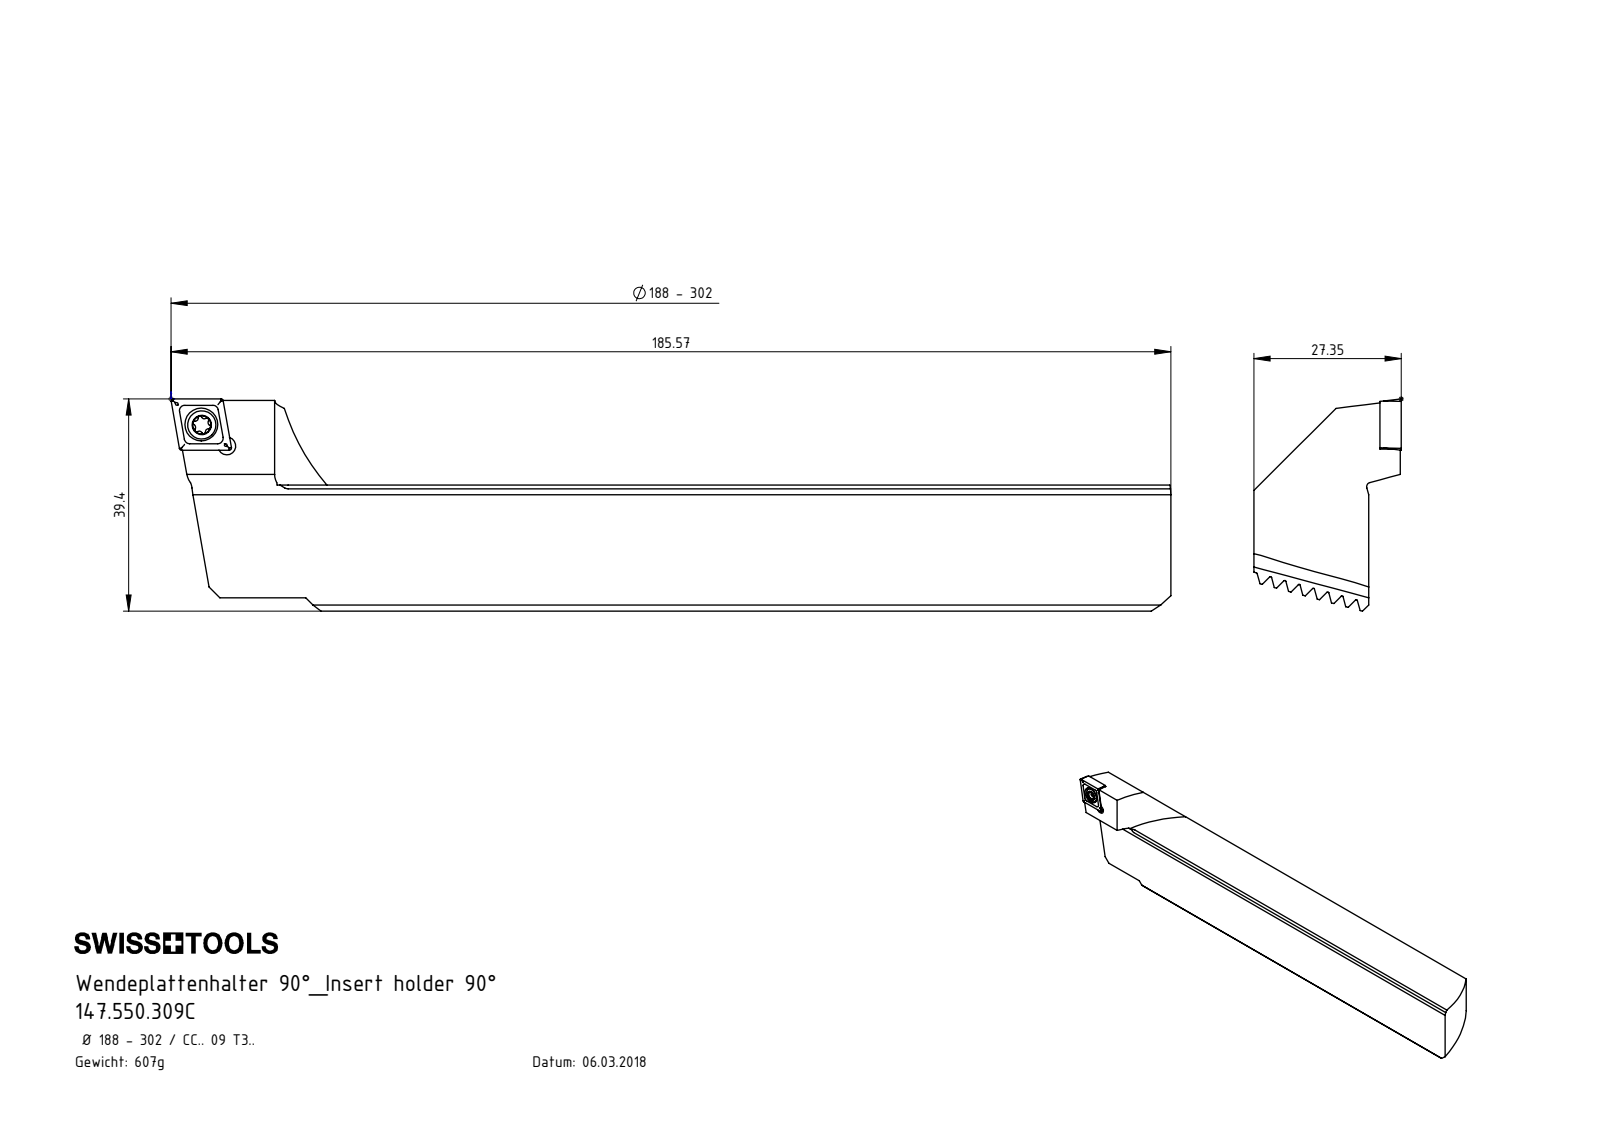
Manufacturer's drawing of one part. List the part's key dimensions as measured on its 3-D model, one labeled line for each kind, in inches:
Part name (STEP PRODUCT): 147.550.309C; WCB-ER2.001.009_A; F00-WCB.188.001_C; CCMT09T304
STEP written by: SolidWorks 2017 (CONFIG_CONTROL_DESIGN)
Units: inches
Bodies: 3 solids, 694 faces (422 planar, 39 cylindrical, 233 other)
Overall size (bounding box): 7.306 × 1.551 × 1.077
Volume: 4.719 in³ · Surface area: 29.34 in²
Round holes (diameter × count): ⌀0.13 ×2, ⌀0.173 ×1, ⌀0.24 ×1
Round bosses / shafts (diameter × count): ⌀0.207 ×1, ⌀0.157 ×1
Partial cylindrical surfaces — rounded edges, fillets, slot ends (radius × count): R0.008 ×8, R0.013 ×6, R0.023 ×6, R1.575 ×3, R0.031 ×1
Main face-to-face distances: 0.094, 0.839, 0.187, 0.281, 0.375, 0.188, 0.281, 0.375, 0.469, 0.563
Hole centre spacings: 0.239, 0.244
